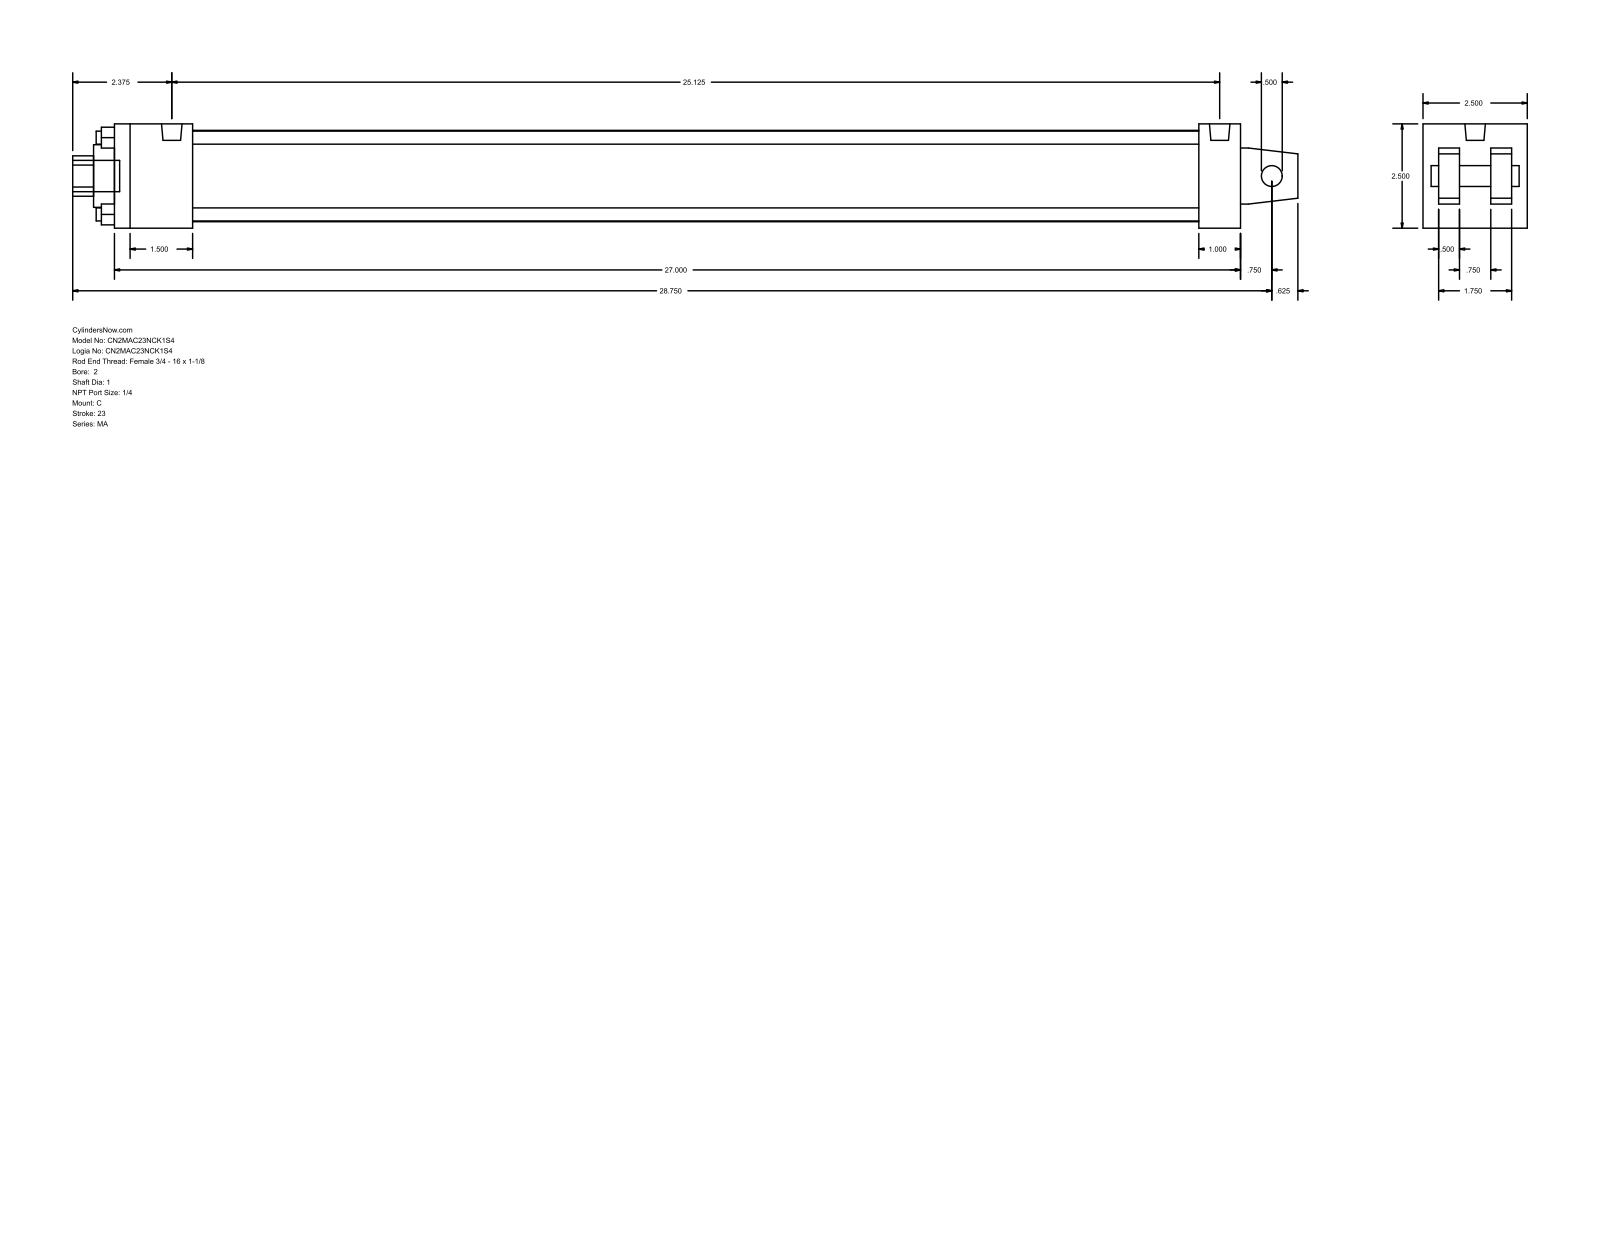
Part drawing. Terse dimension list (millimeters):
name: MA_C__0200_1
written by: GSSL Pune (CONFIG_CONTROL_DESIGN)
unit: mm
bodies: 0 solids, 103 faces (76 planar, 27 cylindrical, 0 other)
size: 746.12 × 63.5 × 63.5
holes: 4× ⌀7.94, 1× ⌀12.7, 1× ⌀25.4, 1× ⌀38.1, 1× ⌀55.63
bosses: 4× ⌀7.94, 2× ⌀12.49, 1× ⌀19.05
rounds: 1× R12.29
face distances: 63.5, 12.7, 685.8, 22.22, 41.28, 9.52, 53.98, 31.76, 47.63, 25.4
hole spacings: 33.05, 46.74, 66.1
